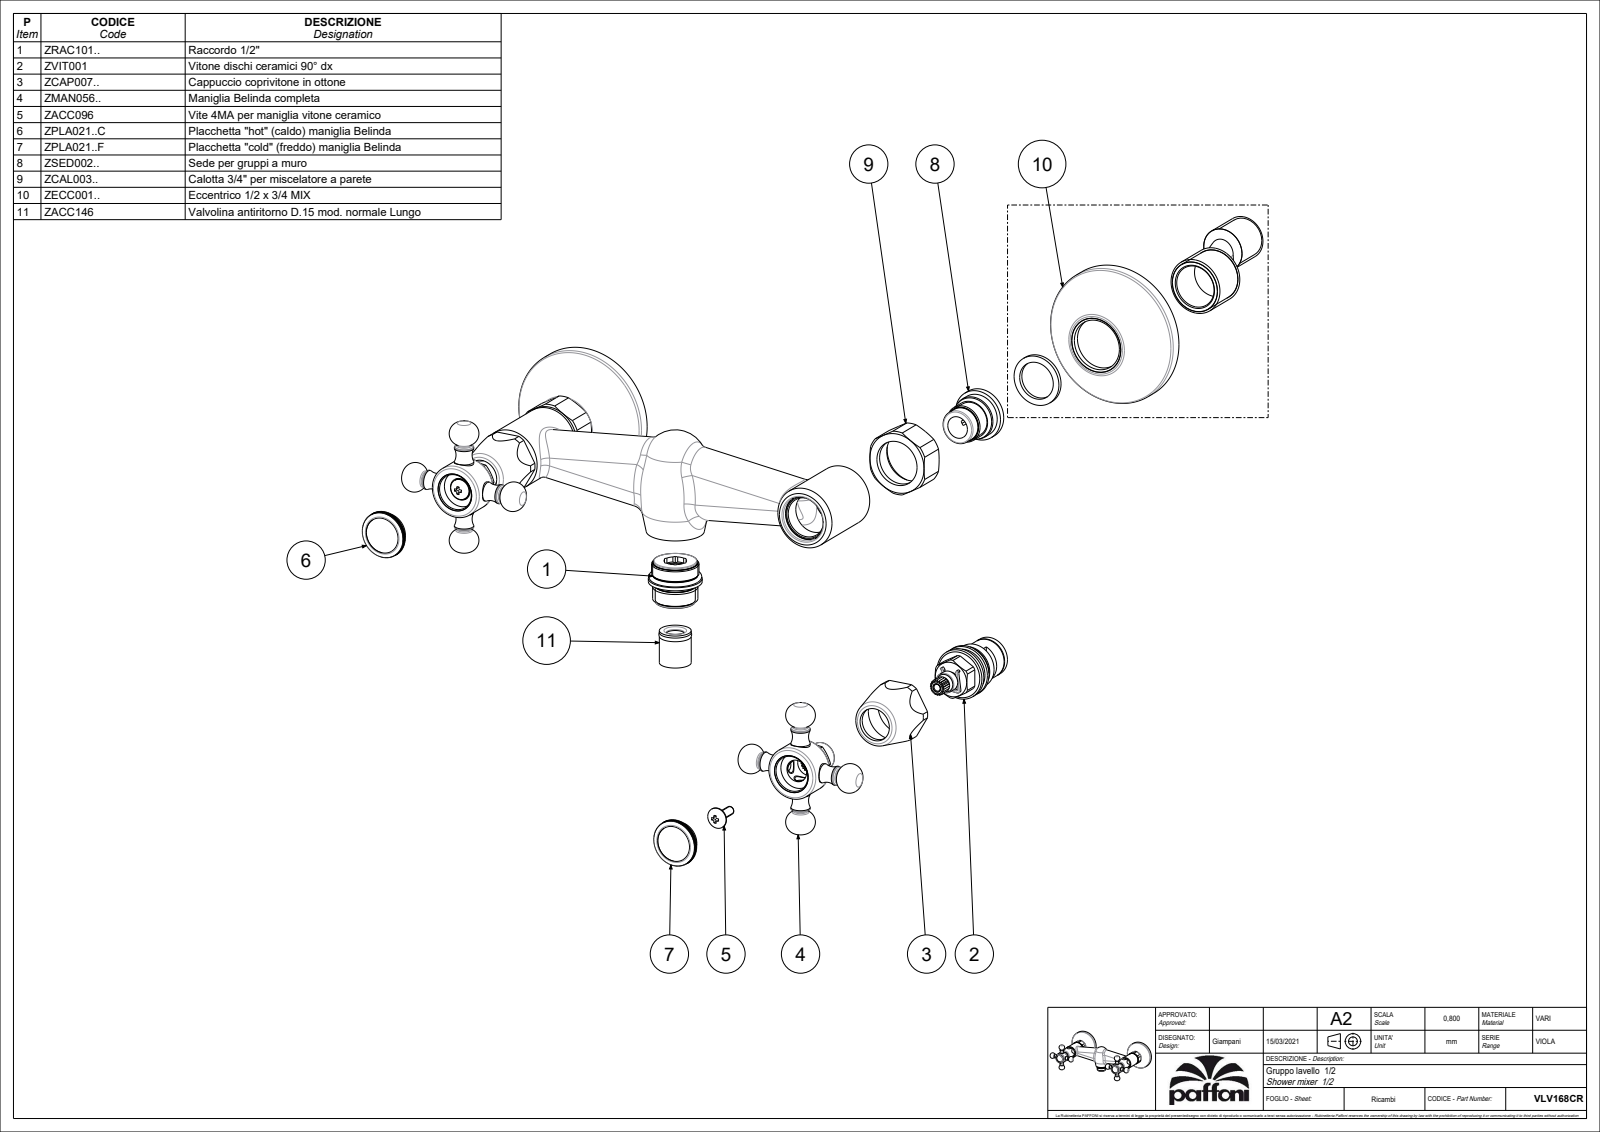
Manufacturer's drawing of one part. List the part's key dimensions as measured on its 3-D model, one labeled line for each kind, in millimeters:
Part name (STEP PRODUCT): VLV168CR
STEP written by: CREO PARAMETRIC BY PTC INC, 2020044 (CONFIG_CONTROL_DESIGN)
Units: millimetres
Bodies: 3 solids, 1377 faces (633 planar, 406 cylindrical, 338 other)
Overall size (bounding box): 223.5 × 124.4 × 70.25
Volume: 220 211 mm³ · Surface area: 77 069 mm²
Round holes (diameter × count): ⌀10.5 ×2, ⌀15.7 ×2, ⌀19 ×2, ⌀21.3 ×2, ⌀23 ×2, ⌀15.1 ×1, ⌀21 ×1
Round bosses / shafts (diameter × count): ⌀25 ×3, ⌀9 ×3, ⌀7 ×3, ⌀65.5 ×2, ⌀29 ×2, ⌀22 ×2, ⌀20.5 ×2, ⌀17.7 ×2
Partial cylindrical surfaces — rounded edges, fillets, slot ends (radius × count): R6.5 ×4, R10 ×4, R3.5 ×2, R15.5 ×2, R5.25 ×1, R12 ×1
Main face-to-face distances: 16.5, 3.5, 10, 26.5, 8.5, 28.5, 12, 1.5, 20, 34
Hole centre spacings: 158
